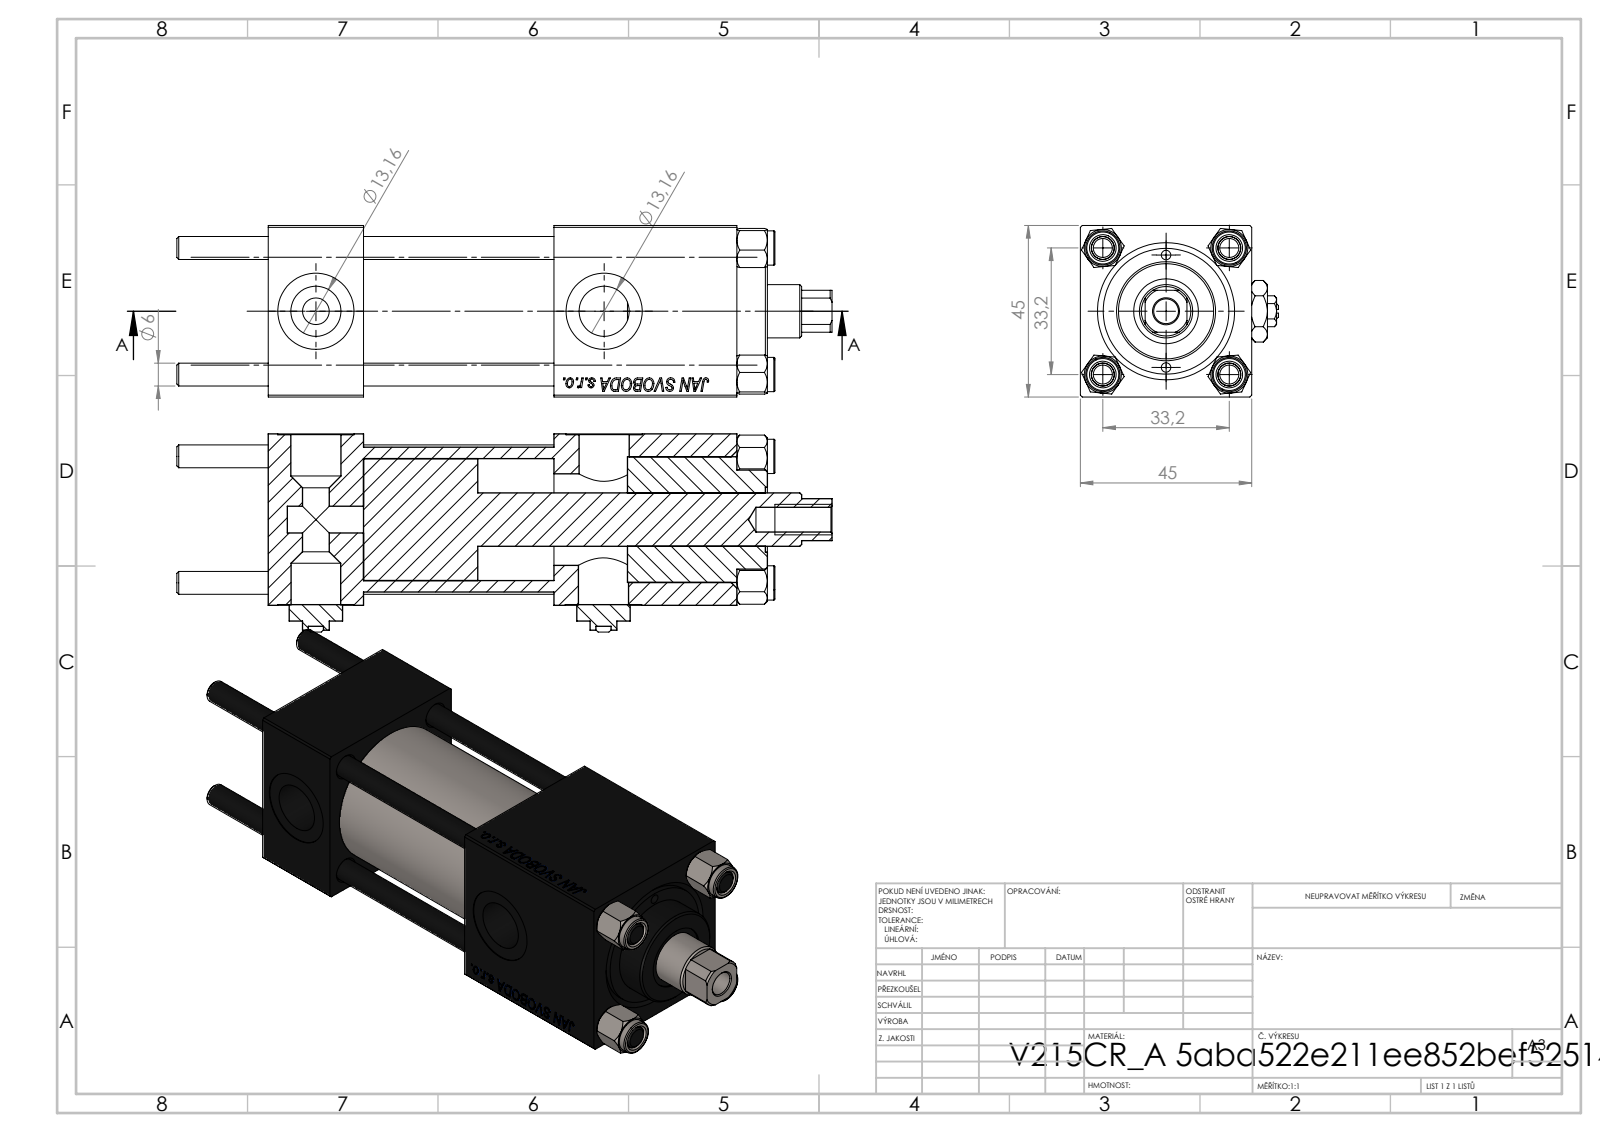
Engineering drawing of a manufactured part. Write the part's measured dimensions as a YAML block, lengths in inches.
part_name: "V215CR_VCP; CR025_012_A_0_G_A_G_M_020_+#_##_TYCINKA; V215CR_BODY_A; V215_VC_A (+2 more)"
step_written_by: "SolidWorks 2019 (CONFIG_CONTROL_DESIGN)"
units: inches
bodies: {solids: 13, faces: 1238, planar: 566, cylindrical: 94, other: 578}
overall_size: [6.772, 2.047, 1.772]
volume: 11.98
surface_area: 115.9
round_holes:
  - {diameter: 0.236, count: 4}
  - {diameter: 0.518, count: 3}
  - {diameter: 0.787, count: 3}
  - {diameter: 0.098, count: 2}
  - {diameter: 0.276, count: 2}
  - {diameter: 0.256, count: 1}
  - {diameter: 0.512, count: 1}
  - {diameter: 0.551, count: 1}
  - {diameter: 0.669, count: 1}
  - {diameter: 0.945, count: 1}
  - {diameter: 1.26, count: 1}
  - {diameter: 1.299, count: 1}
round_bosses_or_shafts:
  - {diameter: 0.354, count: 4}
  - {diameter: 1.496, count: 1}
  - {diameter: 1.024, count: 1}
partial_cylinders:
  - {radius: 0.256, count: 1}
face_to_face_distances: [1.772, 0.984, 4.843, 3.858, 1.969, 2.953, 1.89, 3.713, 2.728, 0.76]
hole_center_spacings: [0.657, 0.924, 1.307, 1.396, 0.581, 1.848, 1.161, 2.972]
